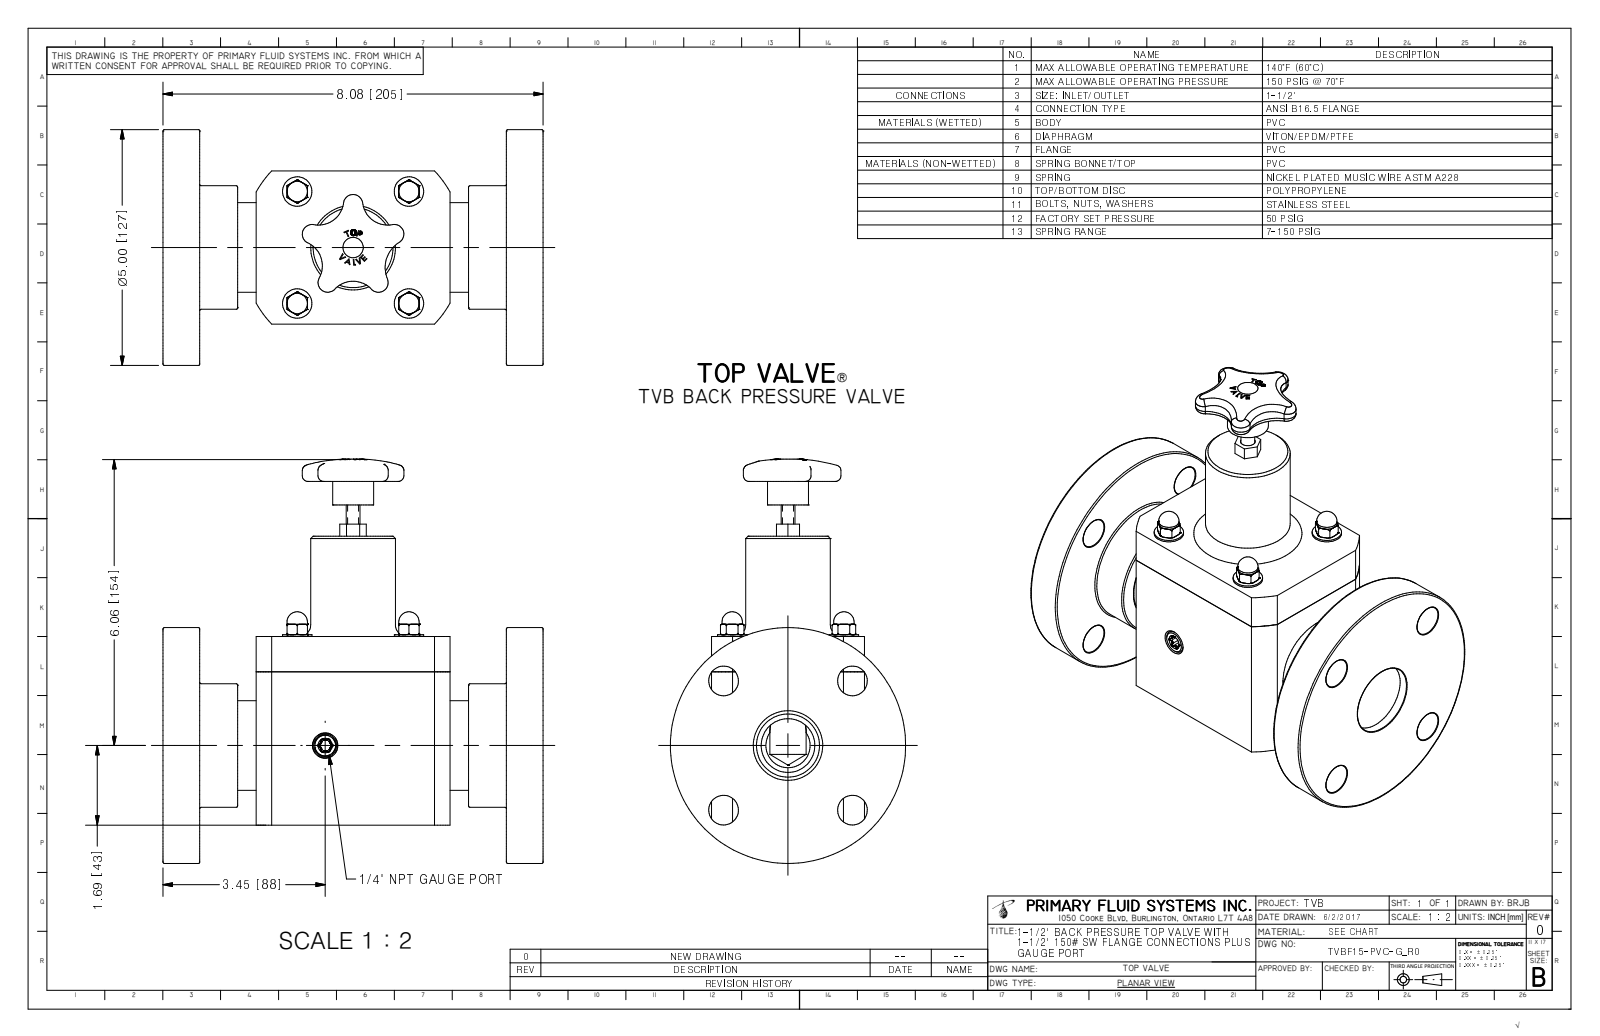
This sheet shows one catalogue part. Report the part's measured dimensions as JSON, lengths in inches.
{"part_name": "TVBF15-PVC-G_R0", "step_written_by": "Autodesk Inventor 2009 (AUTOMOTIVE_DESIGN)", "units": "inches", "bodies": {"solids": 1, "faces": 415, "planar": 160, "cylindrical": 67, "other": 188}, "overall_size": [8.575, 8.08, 5], "volume_in3": 88.73, "surface_area_in2": 280.7, "round_holes": [[0.175, 4], [0.63, 4], [1.476, 1], [1.5, 1]], "round_bosses_or_shafts": [[0.625, 4], [0.433, 4], [0.375, 4], [5, 1], [2.62, 1], [1.9, 1], [1.8, 1], [0.87, 1]], "partial_cylinders_radius": [[0.027, 6], [0.085, 5], [0.205, 5], [0.536, 4], [0.656, 4], [0.625, 1], [0.745, 1], [2.375, 1]], "face_to_face_distances": [0.78, 7.3, 8.08, 3.25, 1.978, 6.103, 1.197, 5.322, 6.52, 4], "hole_center_spacings": [1.937, 2.74, 2.375, 2.375, 3.359, 3.875]}
